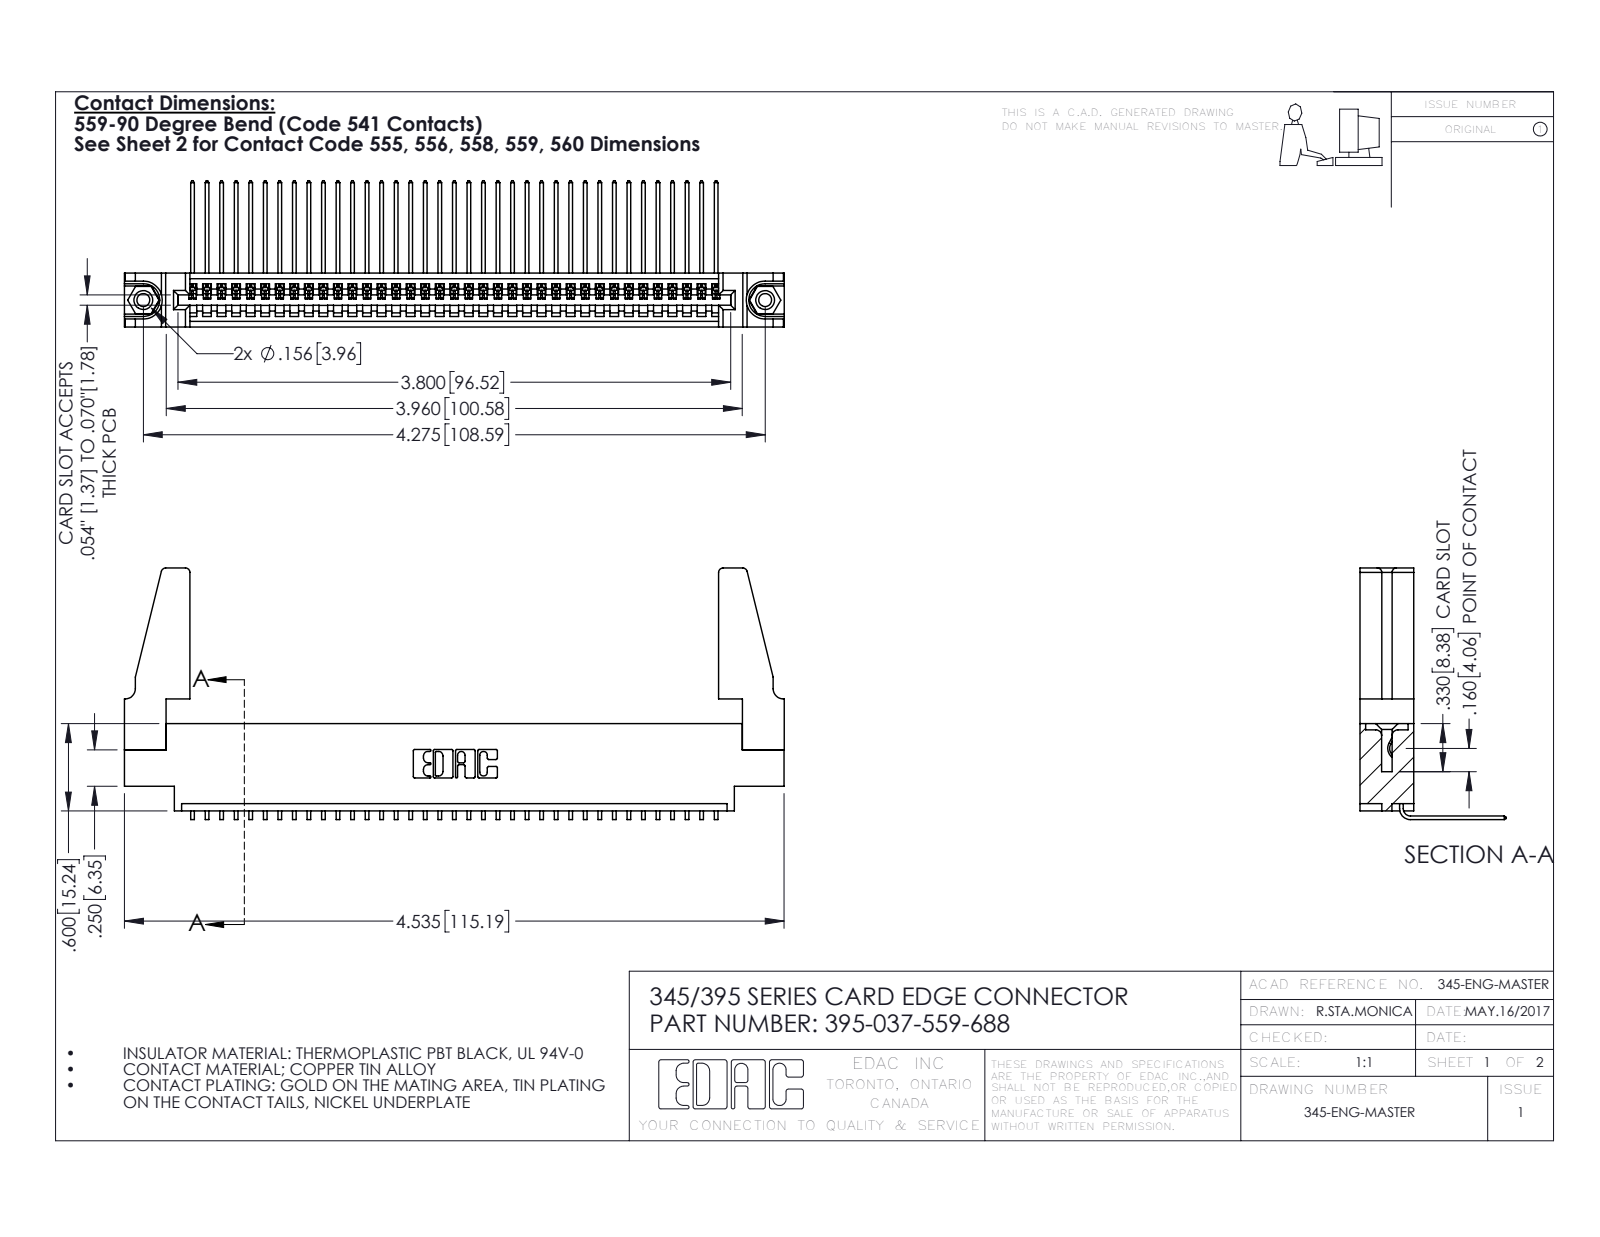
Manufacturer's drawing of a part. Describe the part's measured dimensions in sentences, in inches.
The part is named "345-250-001_345-250-001-102; 345 Part_0.170 Offset - 0.156 Dia-TH; 395-037-559-688; 345-220-078_345-220-088 (+1 more)". Its 3-D file was written by "SolidWorks 2016 (CONFIG_CONTROL_DESIGN)". It is 42 solids with 2474 faces: 1710 planar, 748 cylindrical and 16 other. Overall it measures 4.536 by 1.729 by 1.005 inches. Its volume is 0.864 cubic inches and its surface area 28.54 square inches. Round holes: 2 of diameter 0.089, 2 of diameter 0.125, 2 of diameter 0.156, 1 of diameter 0.064. Round bosses or shafts: 2 of diameter 0.155. Partial cylindrical surfaces (rounded edges, fillets, slot ends): 74 of radius 0.006, 22 of radius 0.01, 8 of radius 0.03, 6 of radius 0.007, 6 of radius 0.031, 3 of radius 0.026, 2 of radius 0.031, 2 of radius 0.04. The main face-to-face distances are 0.37, 0.072, 0.298, 0.098, 0.272, 0.025, 0.2, 0.225, 0.175, 0.149. The hole center spacings are 0.27, 4.039, 4.275.
